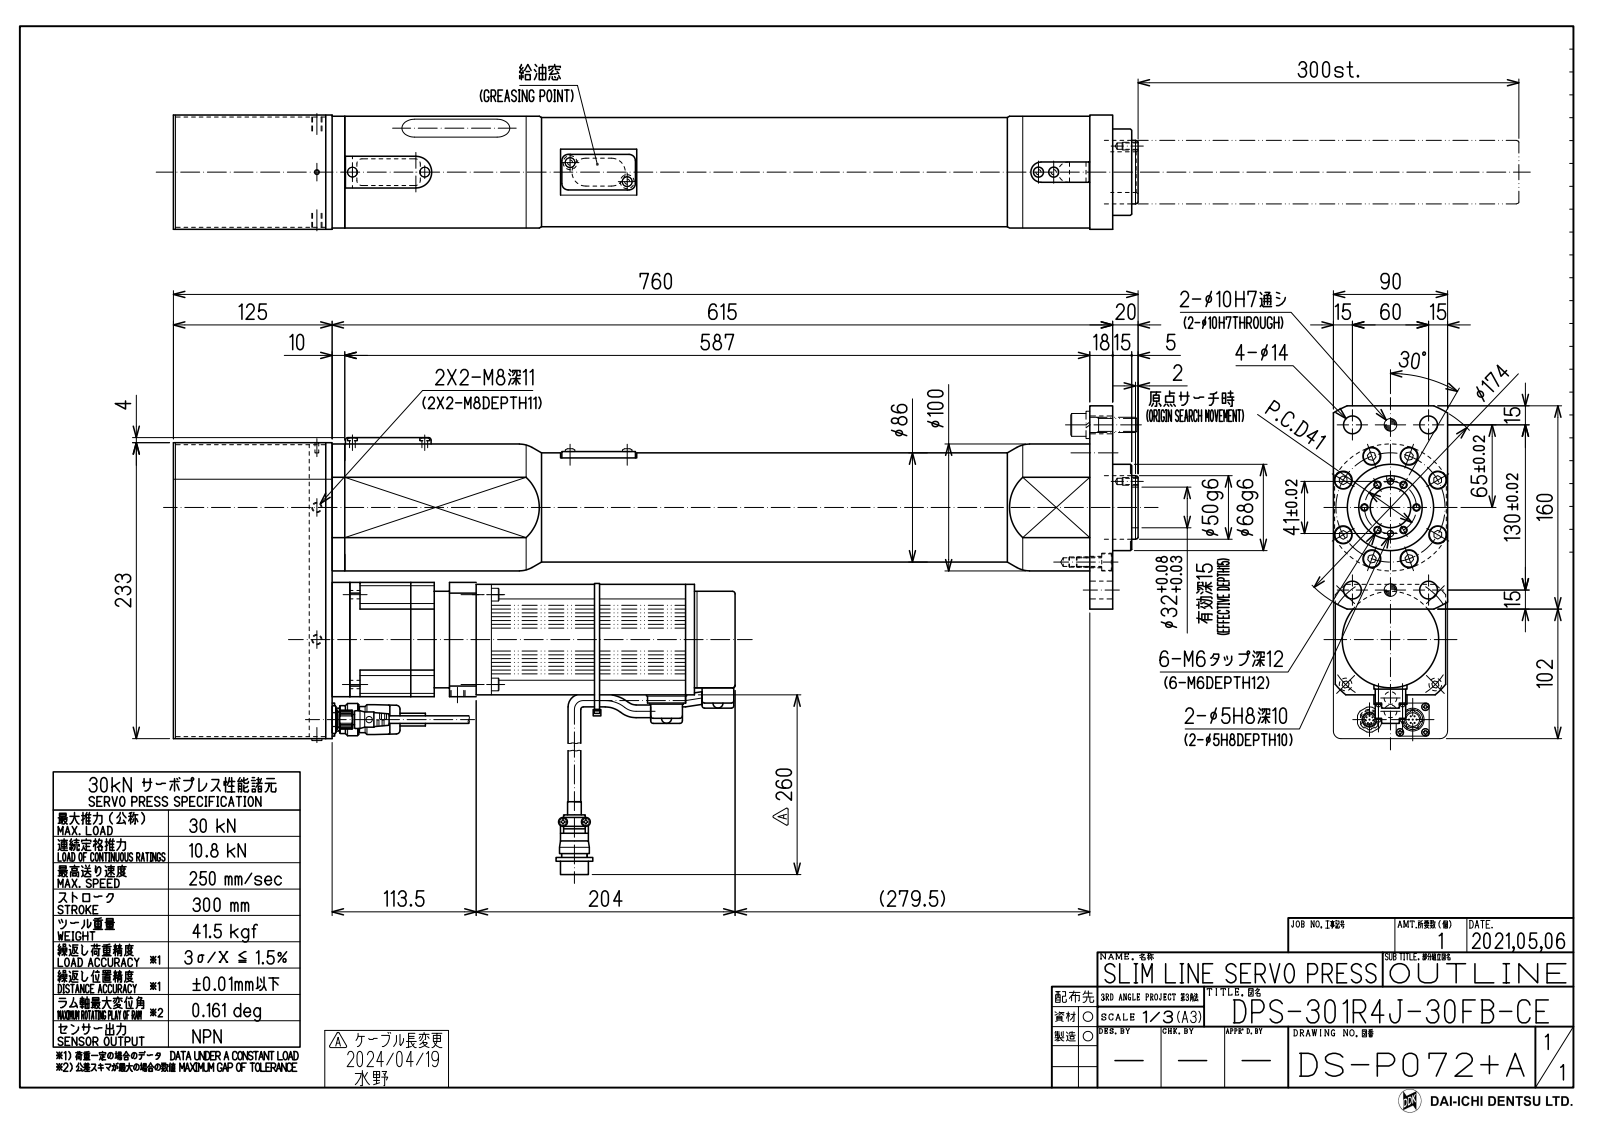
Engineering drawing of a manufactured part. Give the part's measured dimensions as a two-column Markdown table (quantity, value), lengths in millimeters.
| quantity | value |
| --- | --- |
| part name | DPS-301R4J-30FB-CE_(DS-P072)_OUTLINE_20240202 |
| STEP written by | Autodesk Inventor 2023 (CONFIG_CONTROL_DESIGN) |
| units | millimeters |
| bodies | 2 solids, 1770 faces (1003 planar, 500 cylindrical, 267 other) |
| overall size | 760 × 263.5 × 90 |
| volume | 8 709 000 mm³ |
| surface area | 667 953 mm² |
| round holes (diameter × count) | 6.65 × 12, 14 × 12, 4.92 × 10, 5.5 × 10, 9 × 8, 4.2 × 6, 9.5 × 6, 8 × 4, 5 × 3, 4.5 × 2, 10 × 2, 11 × 2 |
| round bosses / shafts (diameter × count) | 8 × 16, 13 × 8, 7 × 6, 3 × 6, 10 × 4, 8.5 × 4, 7.5 × 4, 4 × 4 |
| partial cylindrical surfaces (radius × count) | 0.6 × 48, 1 × 26, 0.3 × 20, 2 × 16, 3 × 10, 4.5 × 10, 5 × 10, 1.5 × 8 |
| main face-to-face distances | 1.5, 90, 3, 1, 88.5, 89, 6, 4.5, 16.5, 18 |
| hole center spacings | 42, 43, 59.39, 60.11, 80.82, 1, 28.65, 28.96 |
